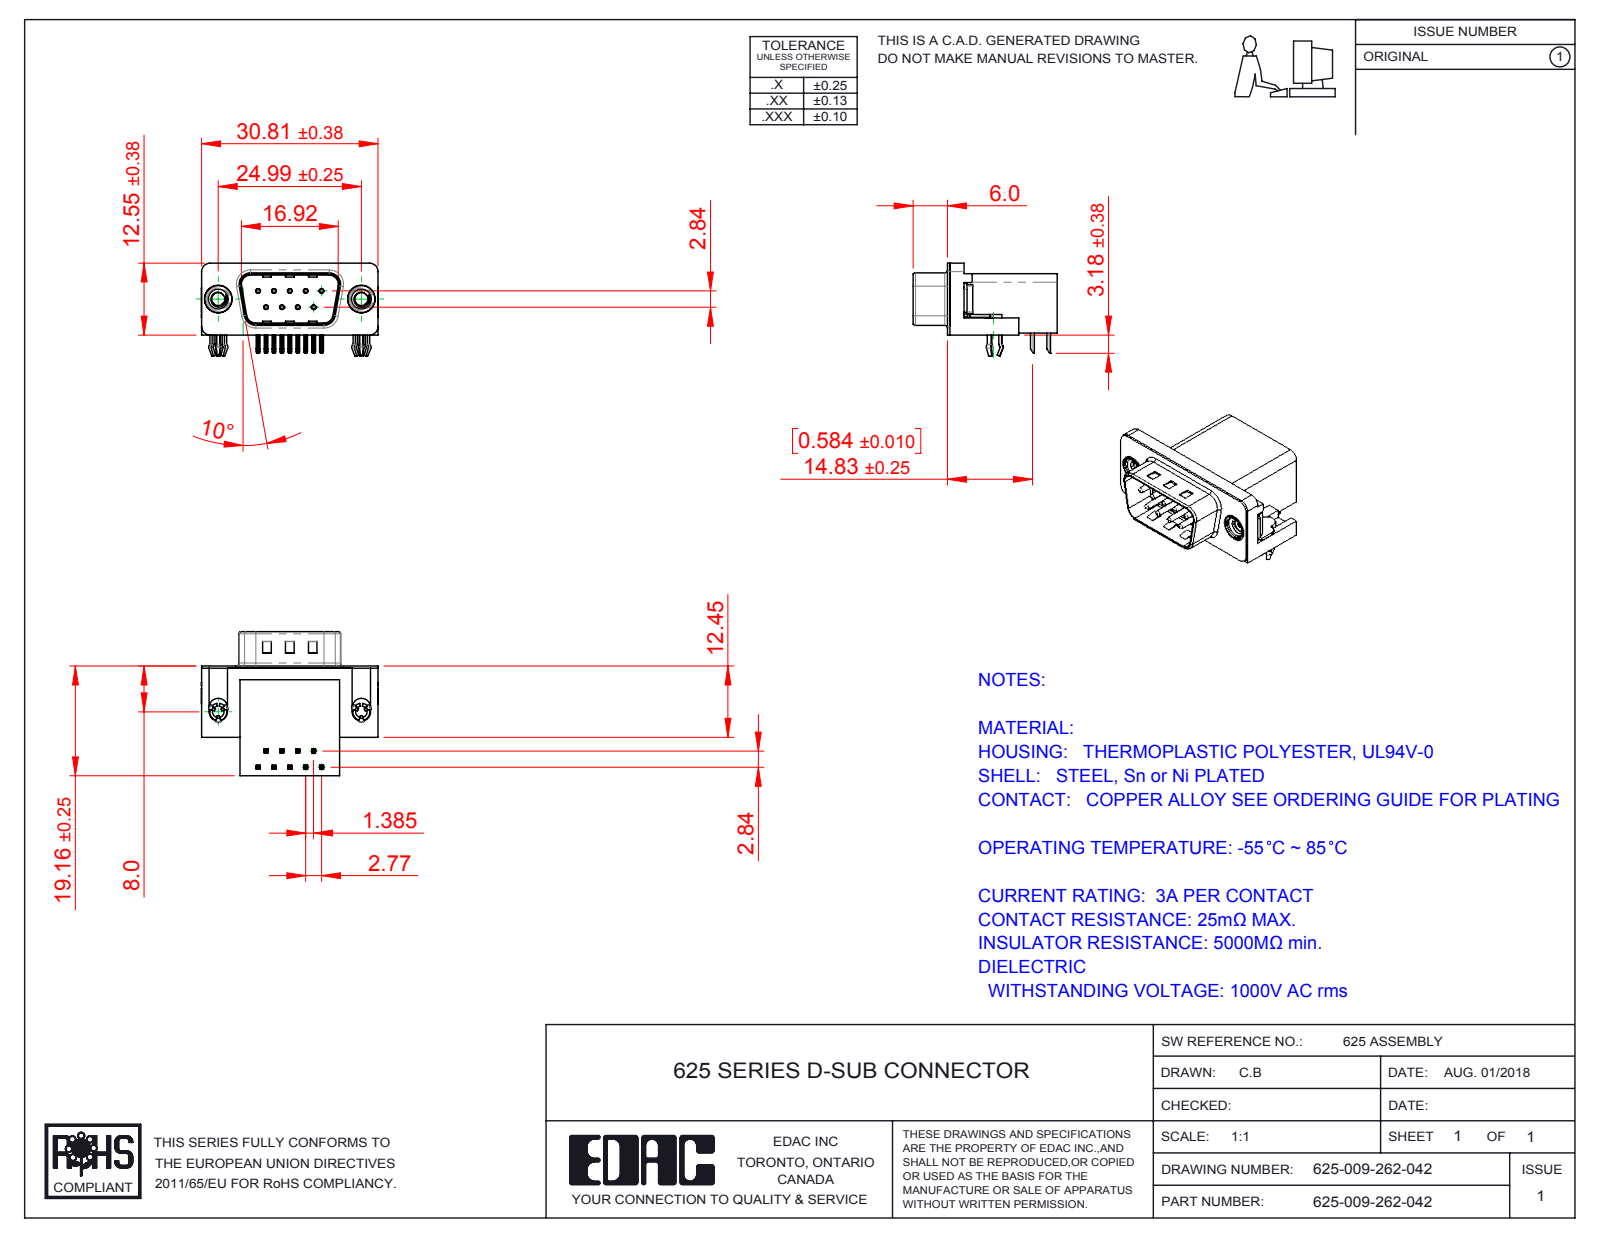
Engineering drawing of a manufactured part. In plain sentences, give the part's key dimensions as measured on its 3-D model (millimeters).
The part is named "625-009-262-042; 625 4-40 Threaded Rivet; 625 3 Prong Board Lock; 625 Contact Top (+3 more)". Its 3-D file was written by "SolidWorks 2016 (CONFIG_CONTROL_DESIGN)". It is 15 solids with 1097 faces: 611 planar, 323 cylindrical and 163 other. Overall it measures 30.89 by 25.16 by 16.25 millimeters. Its volume is 4 485 cubic millimeters and its surface area 5 012 square millimeters. Round holes: 9 of diameter 0.35, 9 of diameter 0.8, 2 of diameter 2, 2 of diameter 2.26, 2 of diameter 4, 2 of diameter 4.8, 2 of diameter 5. Round bosses or shafts: 9 of diameter 0.75, 2 of diameter 4.9, 2 of diameter 4.75, 2 of diameter 3.9, 2 of diameter 3. Partial cylindrical surfaces (rounded edges, fillets, slot ends): 48 of radius 0.25, 18 of radius 0.12, 16 of radius 1, 9 of radius 0.5, 8 of radius 1.5, 8 of radius 1.6, 4 of radius 0.9, 4 of radius 2. The main face-to-face distances are 0.4, 10.34, 18.76, 19.16, 2.9, 16.26, 2.5, 0.35, 10.69, 6.7. The hole center spacings are 3.16, 2.77, 5.54, 5.03, 5.04, 8.31, 7.48, 7.49.
